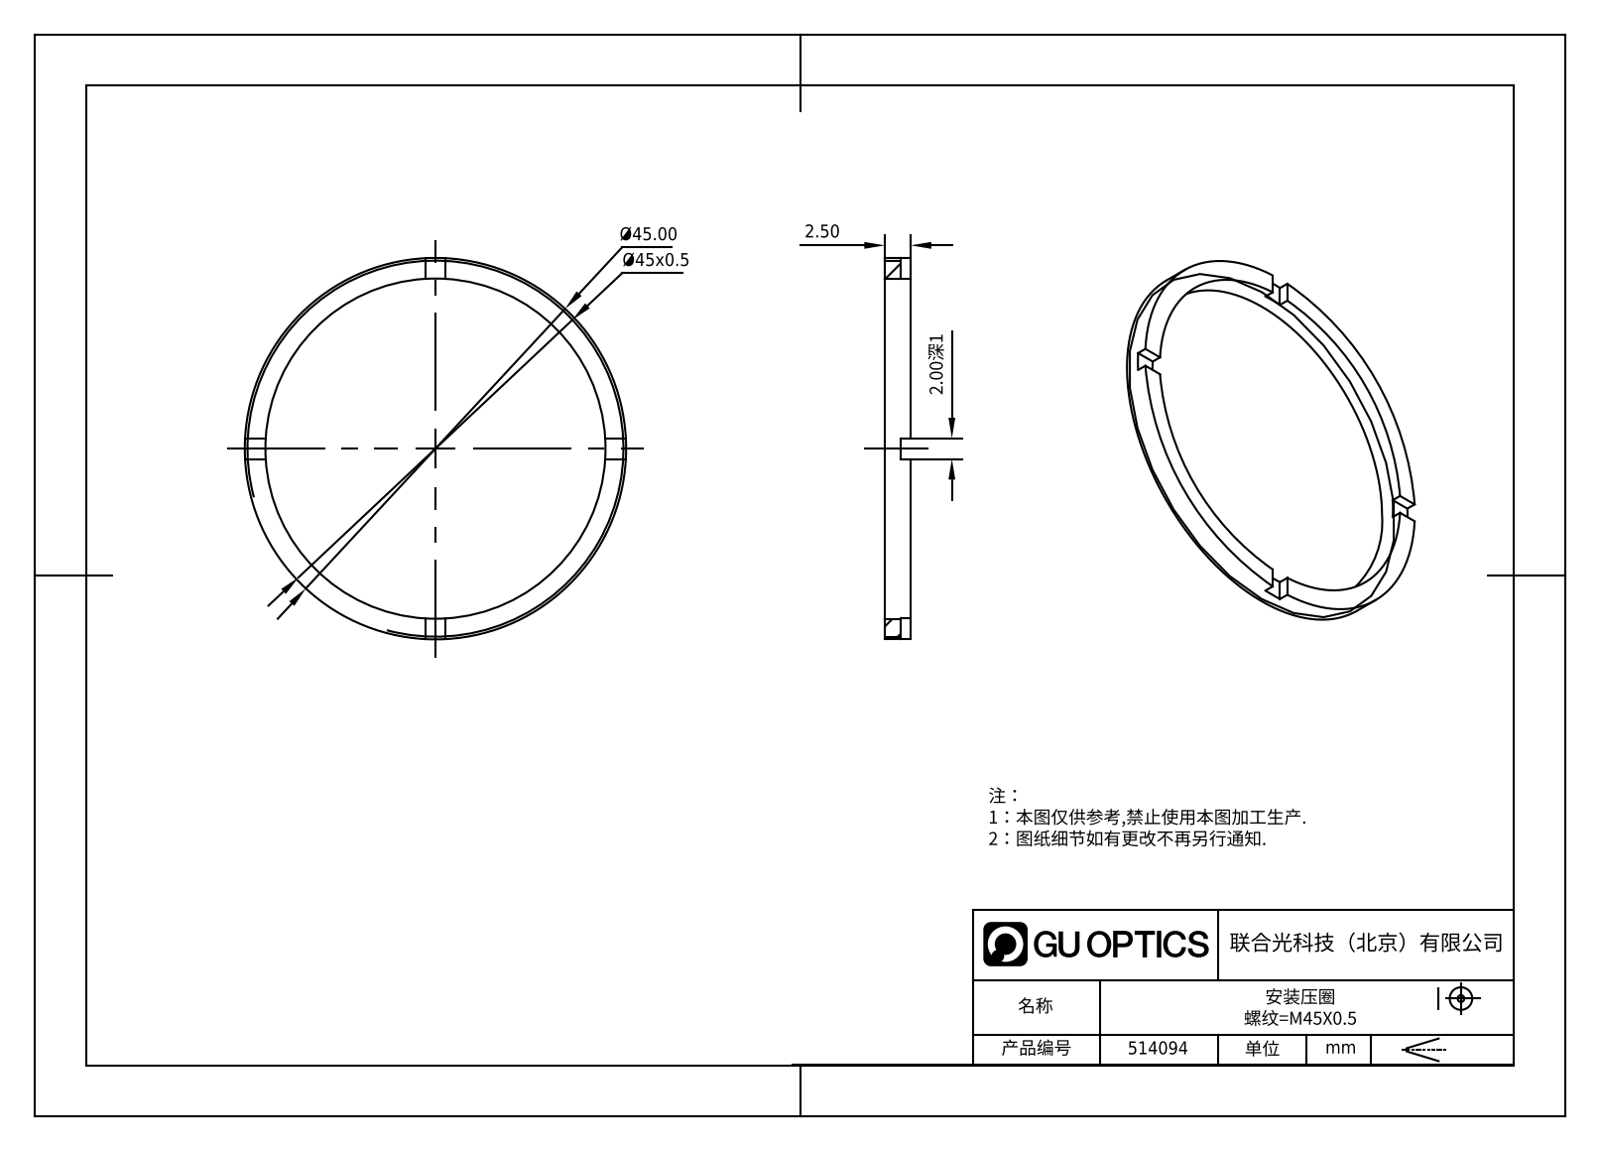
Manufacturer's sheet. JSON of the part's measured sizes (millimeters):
{"part_name": "514094", "step_written_by": "SolidWorks 2020 (CONFIG_CONTROL_DESIGN)", "units": "millimeters", "bodies": {"solids": 1, "faces": 21, "planar": 17, "cylindrical": 4, "other": 0}, "overall_size": [45, 45, 2.5], "volume_mm3": 659, "surface_area_mm2": 1216, "round_holes": [[41, 1]], "round_bosses_or_shafts": [[45, 1]], "face_to_face_distances": [2.5, 1.5, 1, 2]}
